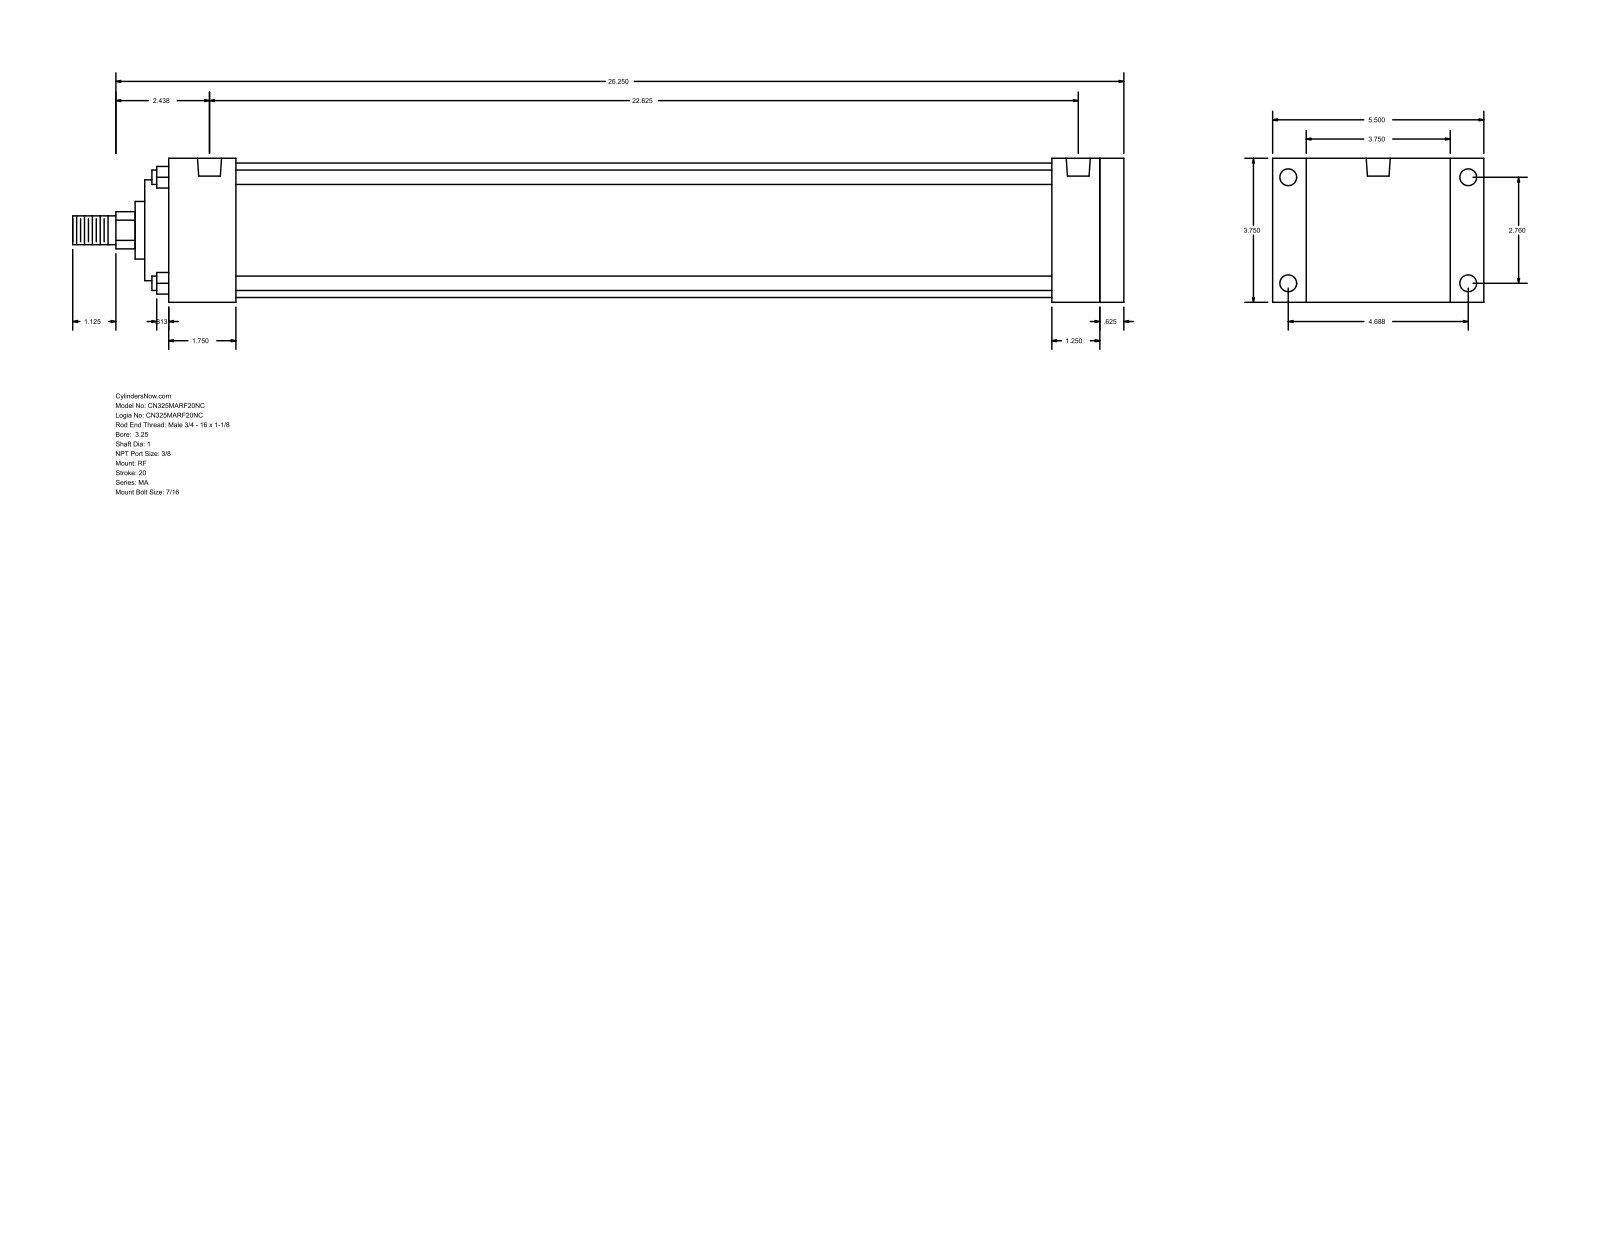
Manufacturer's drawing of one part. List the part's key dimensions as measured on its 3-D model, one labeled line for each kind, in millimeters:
Part name (STEP PRODUCT): MA_RF__0325_1
STEP written by: GSSL Pune (CONFIG_CONTROL_DESIGN)
Units: millimetres
Bodies: 0 solids, 94 faces (65 planar, 29 cylindrical, 0 other)
Overall size (bounding box): 695.33 × 139.7 × 95.25
Round holes (diameter × count): ⌀11.11 ×8, ⌀15.93 ×2
Round bosses / shafts (diameter × count): ⌀9.53 ×4, ⌀88.9 ×1, ⌀66.67 ×1, ⌀38.1 ×1, ⌀25.4 ×1, ⌀19.05 ×1
Partial cylindrical surfaces — rounded edges, fillets, slot ends (radius × count): R12.29 ×1
Main face-to-face distances: 95.24, 631.83, 15.87, 615.96, 22.23, 117.47, 584.2, 31.76, 47.63, 44.46
Hole centre spacings: 4.76, 70.1, 119.06, 138.16, 565.16, 569.92, 574.68
